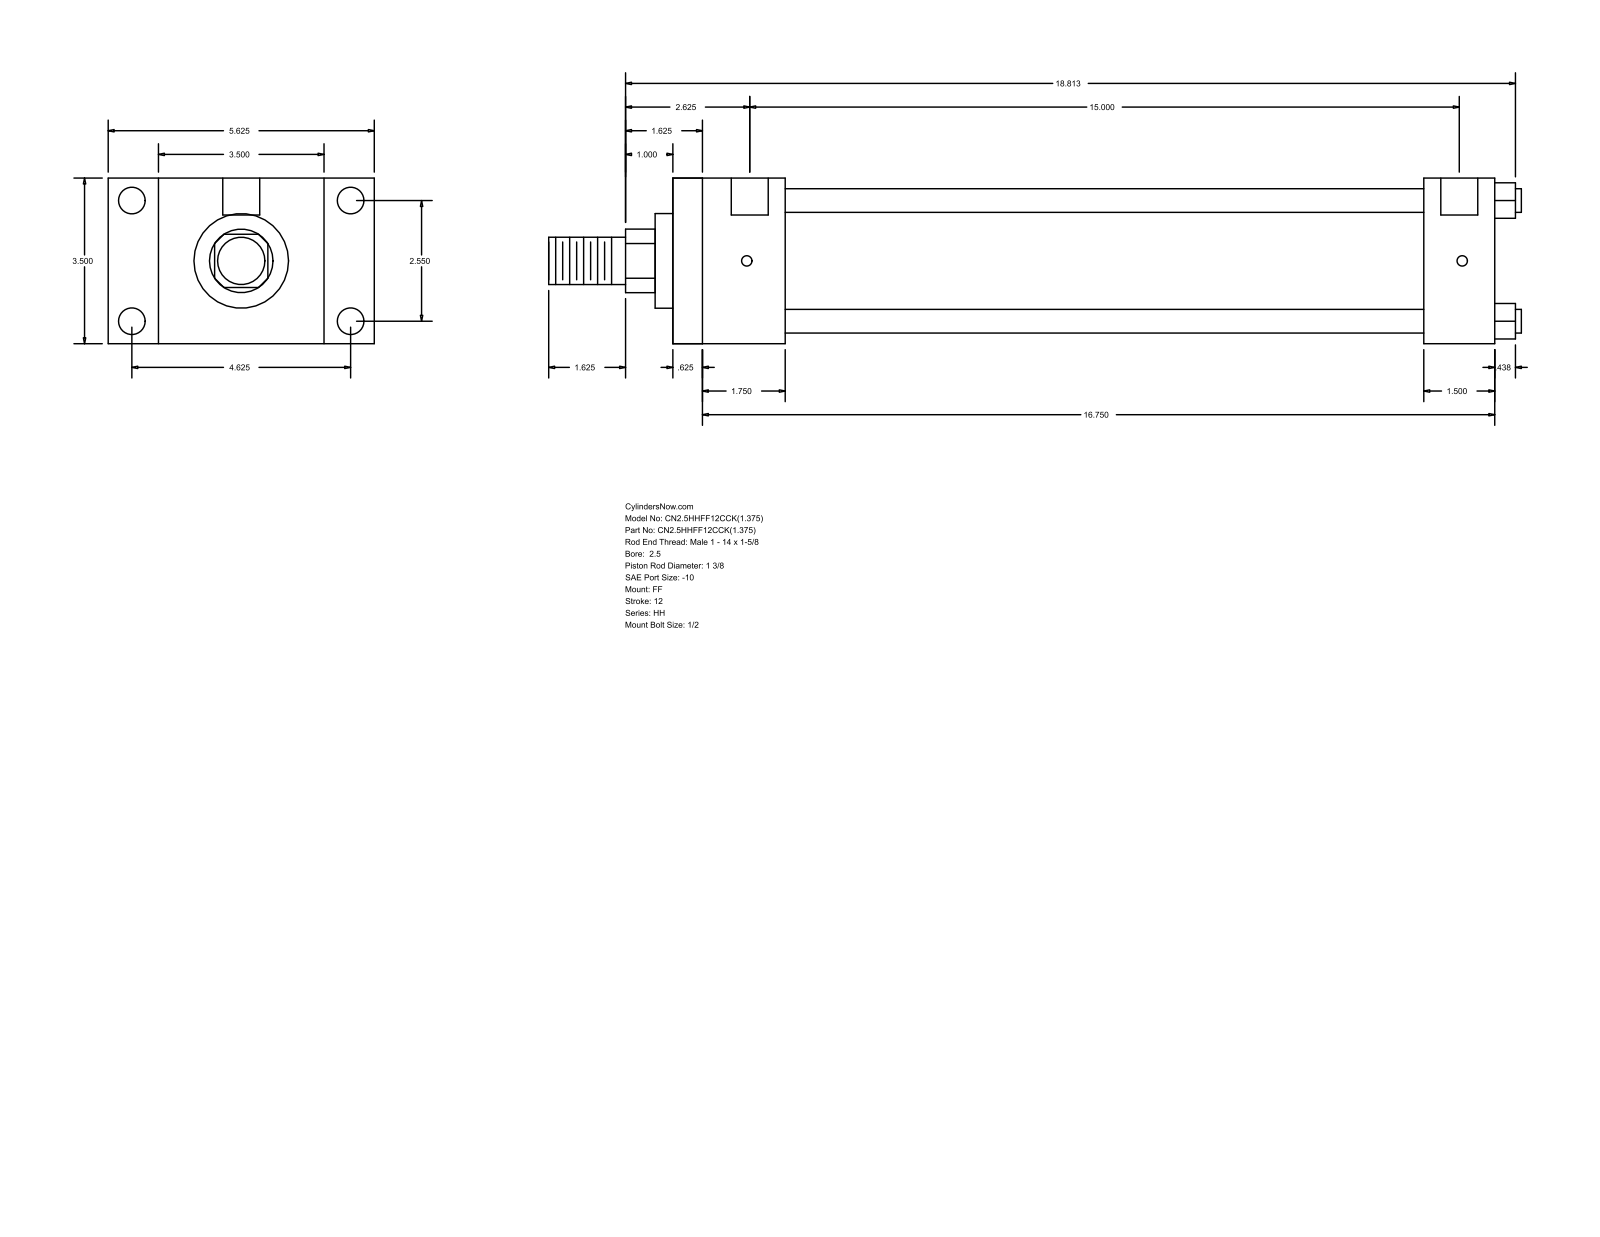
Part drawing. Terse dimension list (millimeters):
name: HH_FF__0250_1.375
written by: GSSL Pune (CONFIG_CONTROL_DESIGN)
unit: mm
bodies: 0 solids, 92 faces (64 planar, 28 cylindrical, 0 other)
size: 522.29 × 142.88 × 88.9
holes: 4× ⌀5.56, 4× ⌀14.3, 2× ⌀19.84
bosses: 4× ⌀12.7, 1× ⌀73.03, 1× ⌀50.8, 1× ⌀34.92, 1× ⌀25.4
rounds: 1× R17.06
face distances: 88.9, 441.33, 15.87, 425.46, 60.32, 44.45, 381.01, 403.22, 387.35, 342.9
hole spacings: 1.58, 64.76, 117.48, 134.15, 382.59, 384.17, 381.01
